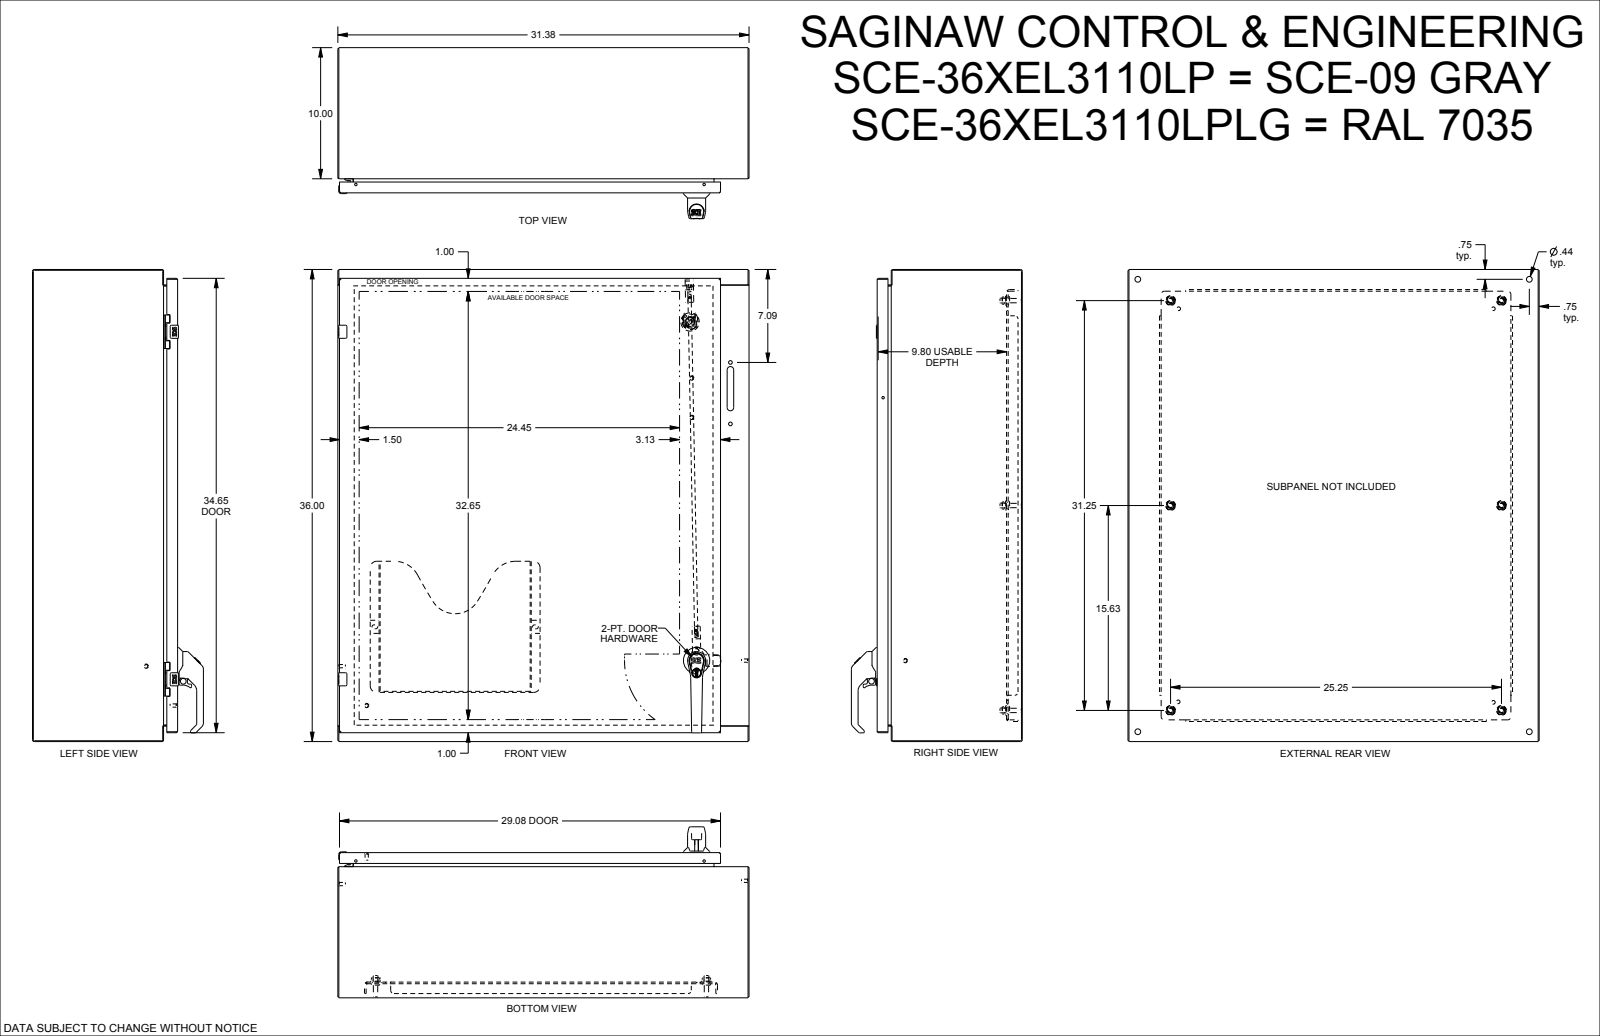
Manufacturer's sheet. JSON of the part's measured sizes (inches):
{"part_name": "SCE-36XEL3110LPLG", "step_written_by": "SolidWorks 2019 (CONFIG_CONTROL_DESIGN)", "units": "inches", "bodies": {"solids": 0, "faces": 4750, "planar": 1773, "cylindrical": 1244, "other": 1733}, "overall_size": [36, 31.375, 13.041], "round_holes": [[0.281, 6], [0.367, 6], [0.5, 6], [0.266, 5], [0.172, 4], [0.205, 4], [0.244, 4], [0.375, 4], [0.437, 4], [0.25, 3], [0.04, 2], [0.138, 2]], "round_bosses_or_shafts": [[0.248, 8], [0.366, 6], [0.332, 6], [0.17, 6], [0.25, 5], [0.24, 4], [0.563, 3], [0.196, 3]], "partial_cylinders_radius": [[0.03, 71], [0.015, 50], [0.01, 44], [0.02, 43], [0.02, 36], [0.039, 30], [0.005, 26], [0.04, 25]], "face_to_face_distances": [0.075, 0.075, 10.998, 10.923, 11.073, 10.998, 1.2, 9.873, 0.125, 9.923], "hole_center_spacings": [0.985, 26.5, 0.493, 0.02, 0.494, 4.493, 0.472, 0.725]}
